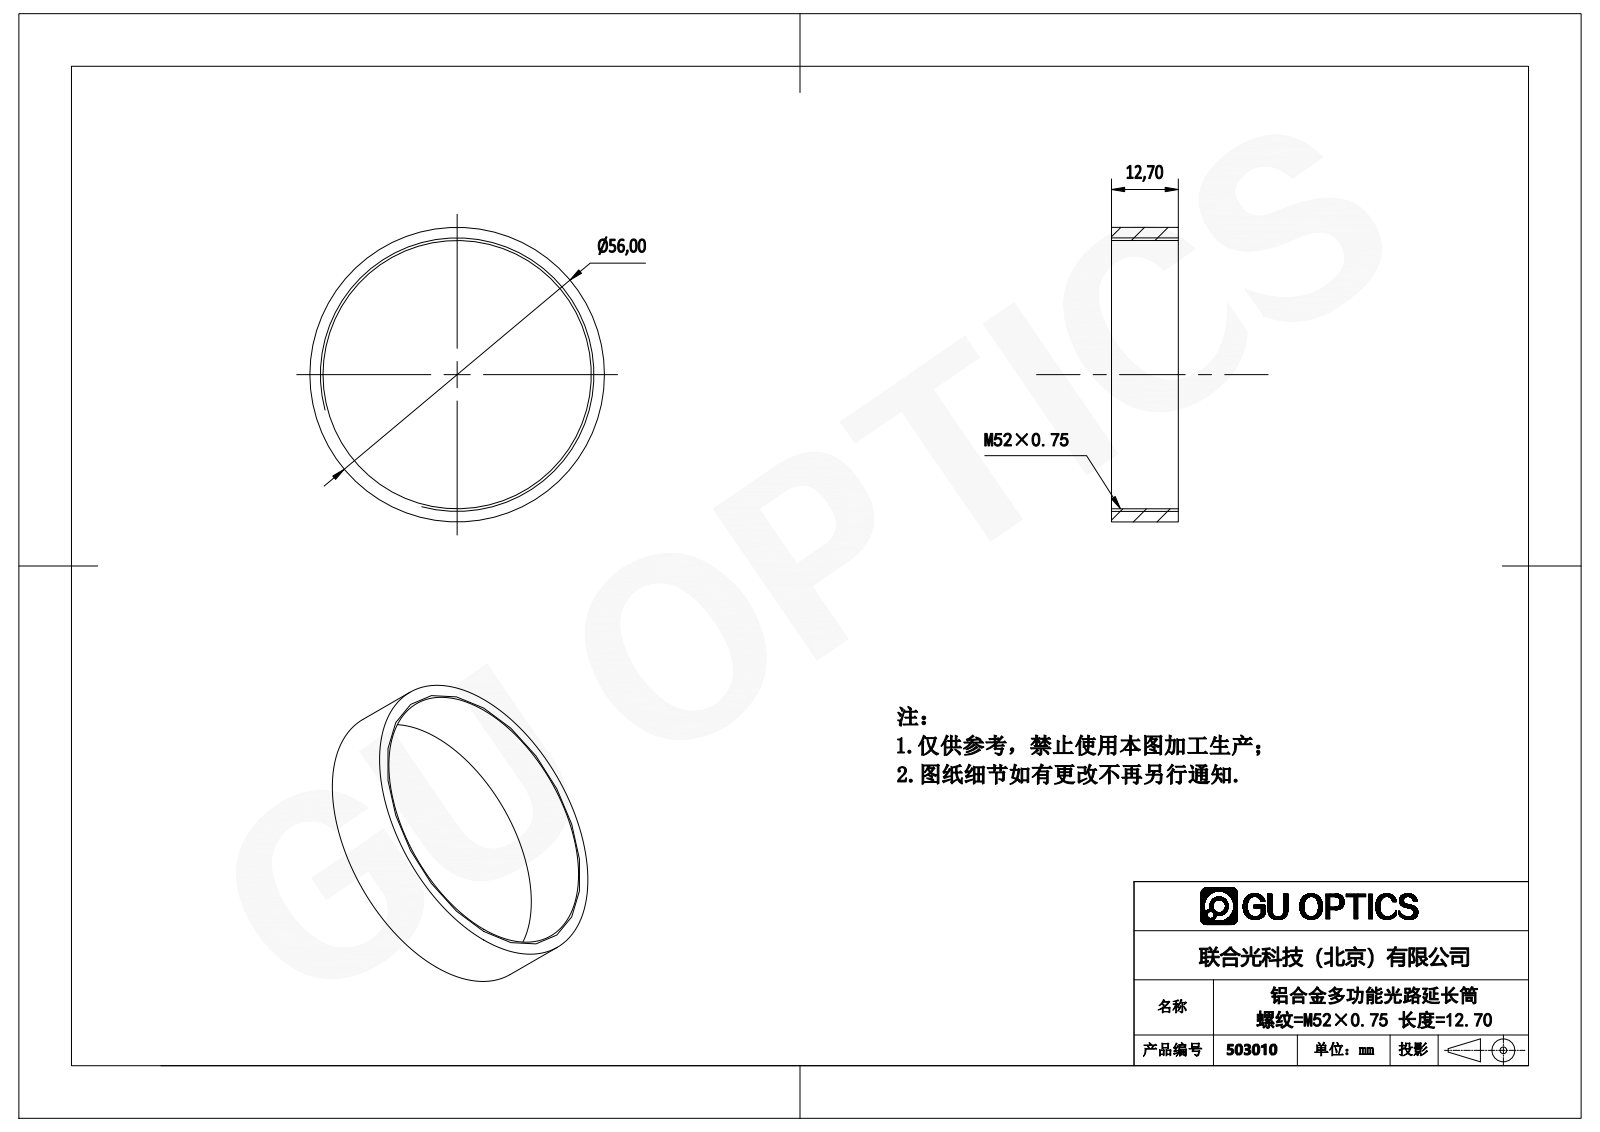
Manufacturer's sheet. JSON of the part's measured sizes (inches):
{"part_name": "503010", "step_written_by": "SolidWorks 2016 (AUTOMOTIVE_DESIGN)", "units": "inches", "bodies": {"solids": 1, "faces": 6, "planar": 2, "cylindrical": 4, "other": 0}, "overall_size": [2.205, 2.205, 0.5], "volume_in3": 0.326, "surface_area_in2": 7.919, "round_holes": [[2.008, 1]], "round_bosses_or_shafts": [[2.205, 1]], "face_to_face_distances": [0.5]}
